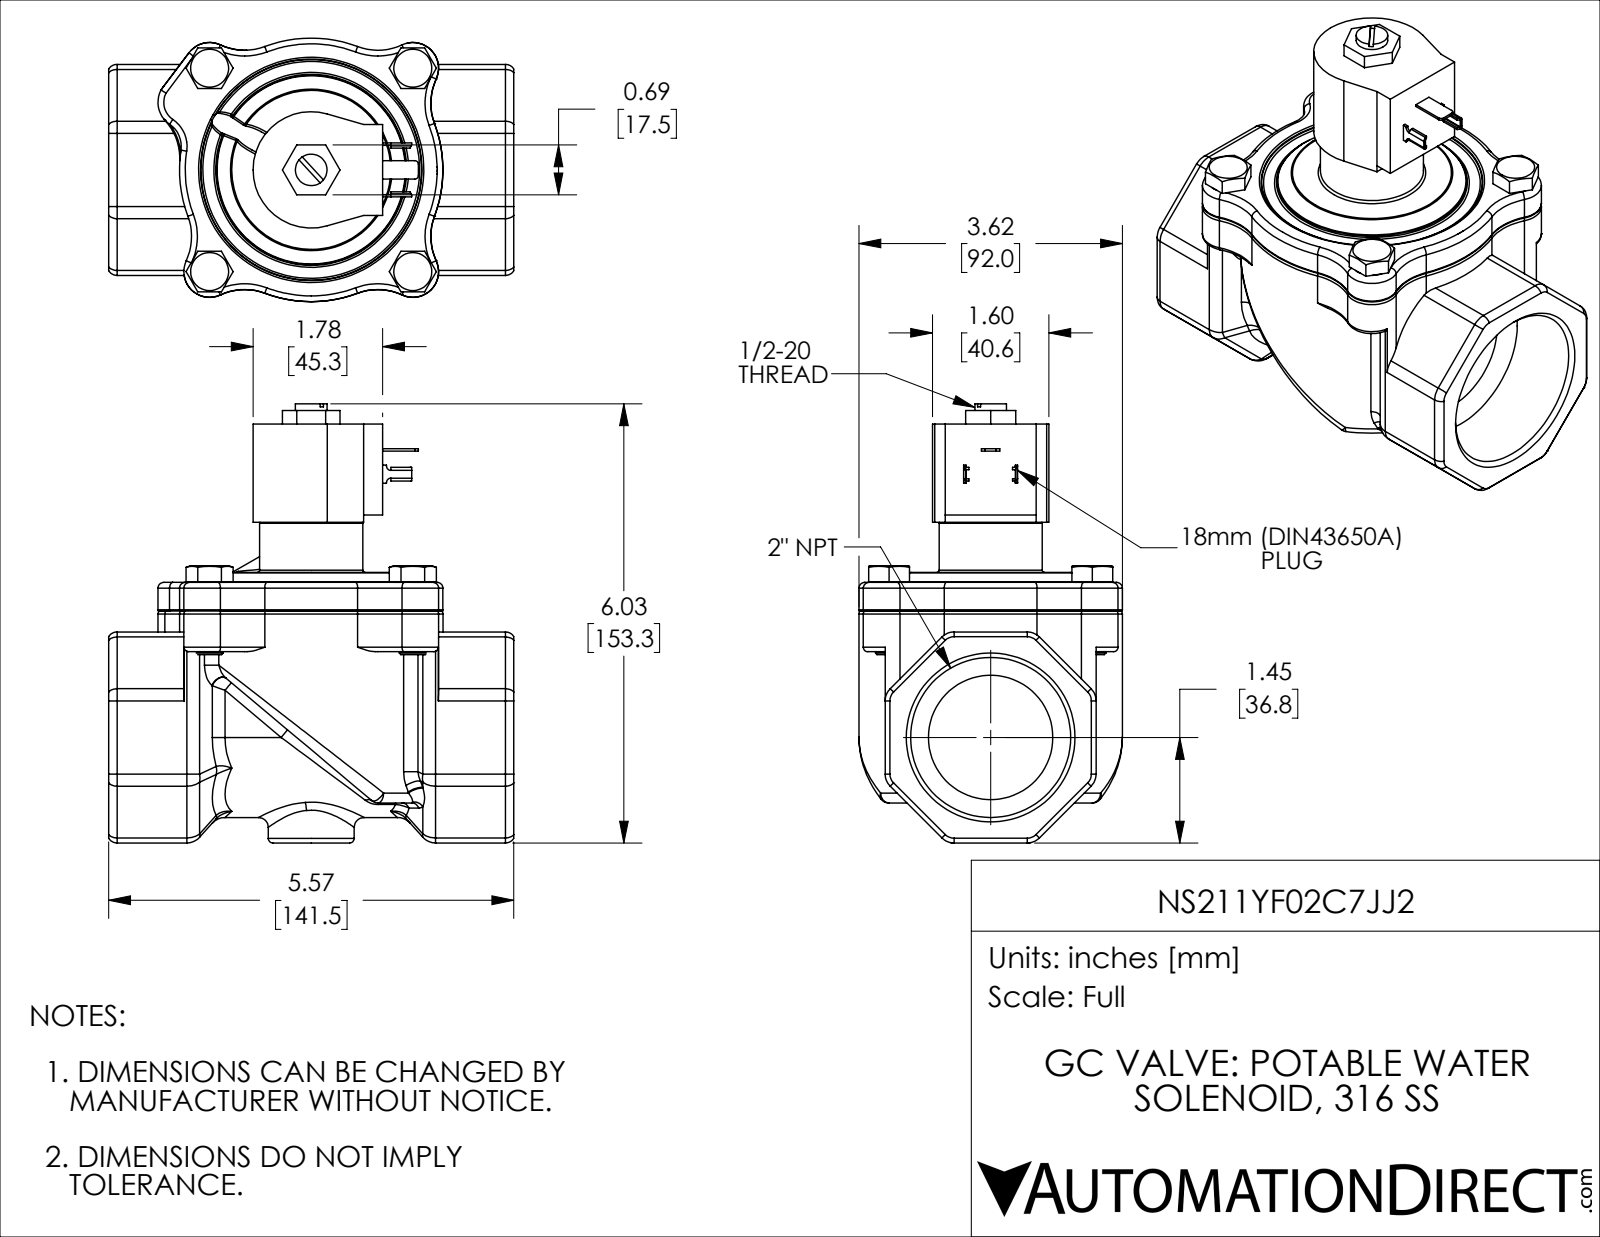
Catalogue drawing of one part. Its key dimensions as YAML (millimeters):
part_name: "NS211YF02C7JJ2"
step_written_by: "SolidWorks 2018 (AUTOMOTIVE_DESIGN)"
units: millimeters
bodies: {solids: 9, faces: 606, planar: 166, cylindrical: 205, other: 235}
overall_size: [153.3, 141.5, 92]
volume: 611200
surface_area: 110800
round_holes:
  - {diameter: 7.9, count: 4}
  - {diameter: 11, count: 4}
  - {diameter: 3, count: 1}
  - {diameter: 3.2, count: 1}
  - {diameter: 6, count: 1}
  - {diameter: 11, count: 1}
  - {diameter: 12.8, count: 1}
  - {diameter: 21.5, count: 1}
  - {diameter: 24.1, count: 1}
  - {diameter: 43.4, count: 1}
  - {diameter: 55.9, count: 1}
  - {diameter: 73, count: 1}
round_bosses_or_shafts:
  - {diameter: 12.8, count: 4}
  - {diameter: 9.4, count: 4}
  - {diameter: 76.8, count: 1}
  - {diameter: 36, count: 1}
  - {diameter: 30, count: 1}
partial_cylinders:
  - {radius: 3.5, count: 29}
  - {radius: 6, count: 28}
  - {radius: 20, count: 15}
  - {radius: 9, count: 8}
  - {radius: 0.2, count: 4}
  - {radius: 1, count: 4}
  - {radius: 1.3, count: 2}
  - {radius: 1.5, count: 2}
face_to_face_distances: [3, 56.1, 85.4, 73.7, 73.7, 13, 10, 34.3, 34, 31]
hole_center_spacings: [50.2, 50.2, 71, 71, 50.2, 59.7, 71, 71]
